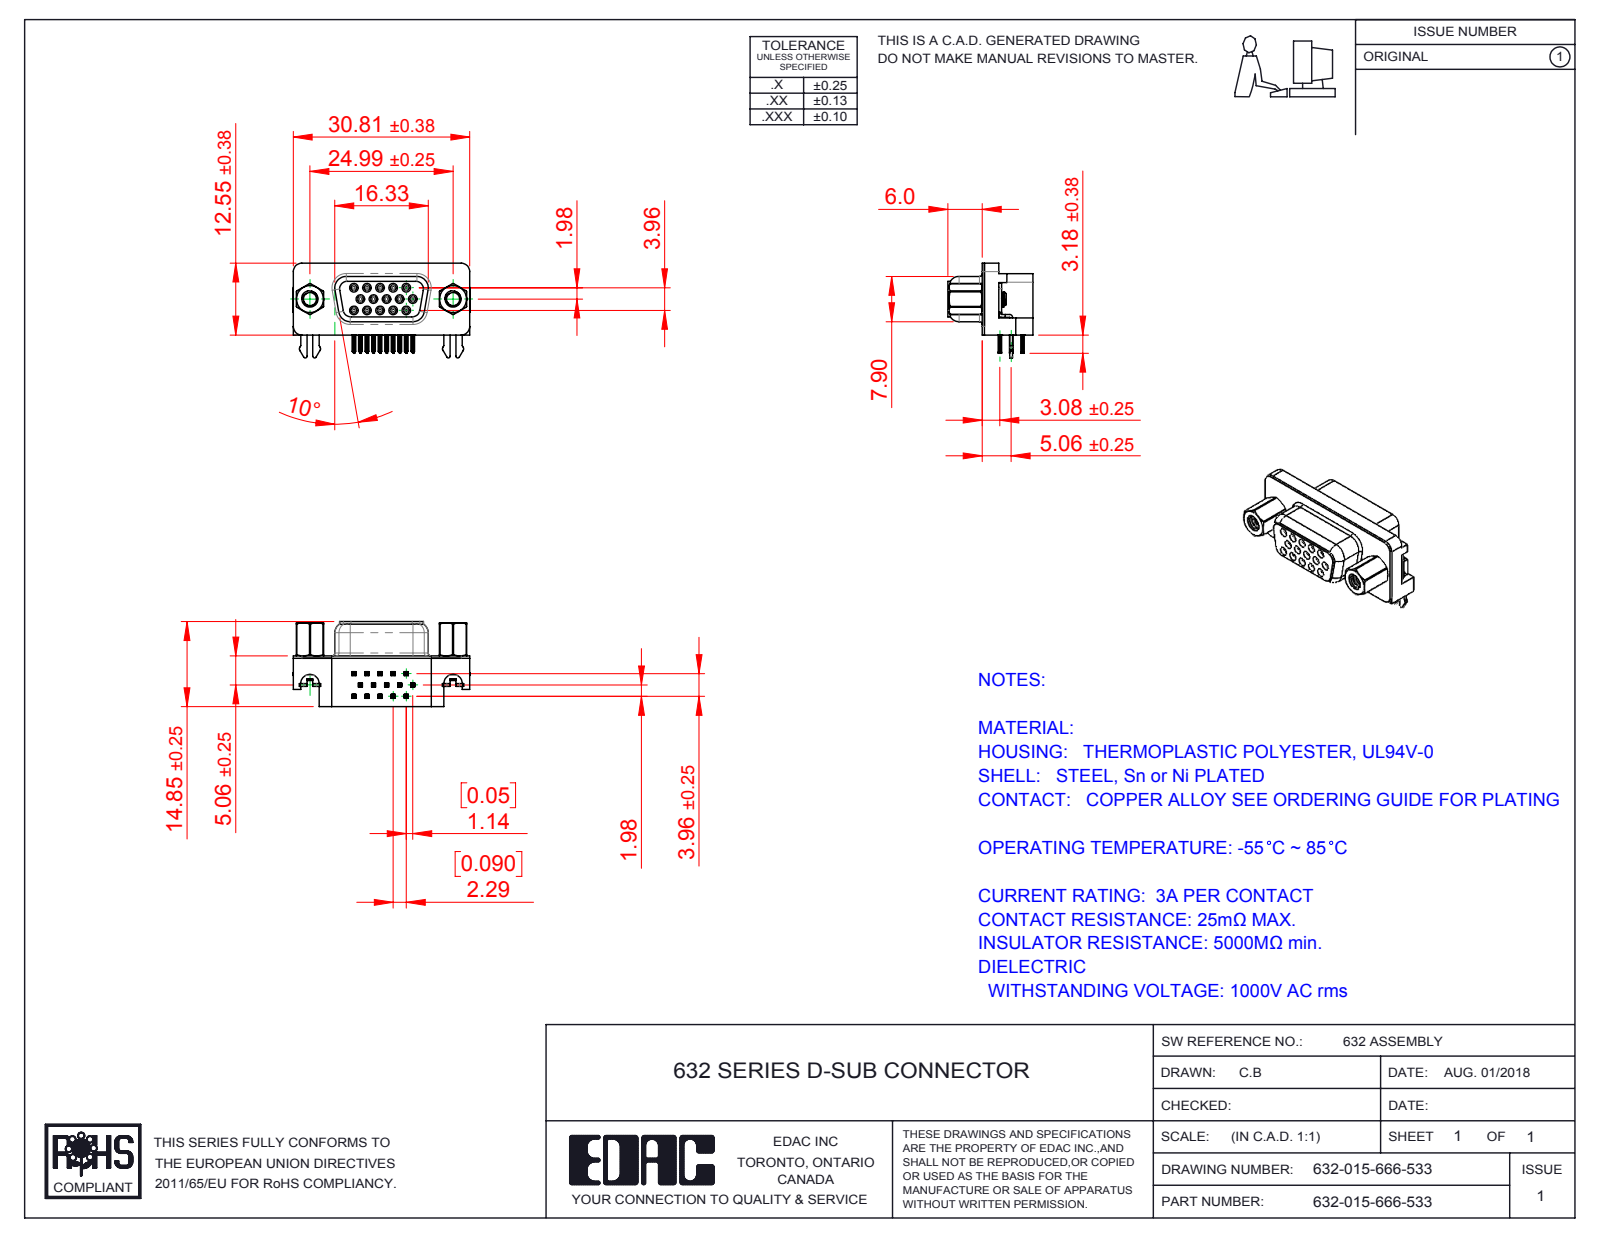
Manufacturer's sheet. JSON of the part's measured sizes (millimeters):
{"part_name": "632 4-40 Hex Standoff 5; 632 Contact Middle; 632-015-666-503; 632 Contact Bottom (+4 more)", "step_written_by": "SolidWorks 2016 (CONFIG_CONTROL_DESIGN)", "units": "millimeters", "bodies": {"solids": 21, "faces": 2376, "planar": 996, "cylindrical": 646, "other": 734}, "overall_size": [30.89, 16.55, 14.85], "volume_mm3": 3051, "surface_area_mm2": 5180, "round_holes": [[0.8, 15], [0.9, 15], [2.29, 2], [4, 2], [4.8, 2], [5, 2]], "round_bosses_or_shafts": [[1.2, 15], [4.9, 2], [2.79, 2]], "partial_cylinders_radius": [[0.1, 120], [0.15, 60], [0.35, 30], [0.34, 15], [1, 11], [0.28, 10], [0.5, 10], [1.35, 8]], "face_to_face_distances": [0.4, 1.98, 8.45, 8.85, 2.9, 2.5, 5.95, 6.7, 7.05, 3.17], "hole_center_spacings": [2.28, 2.29, 3.96, 4.57, 6.05, 3.97, 4.58, 6.86]}
